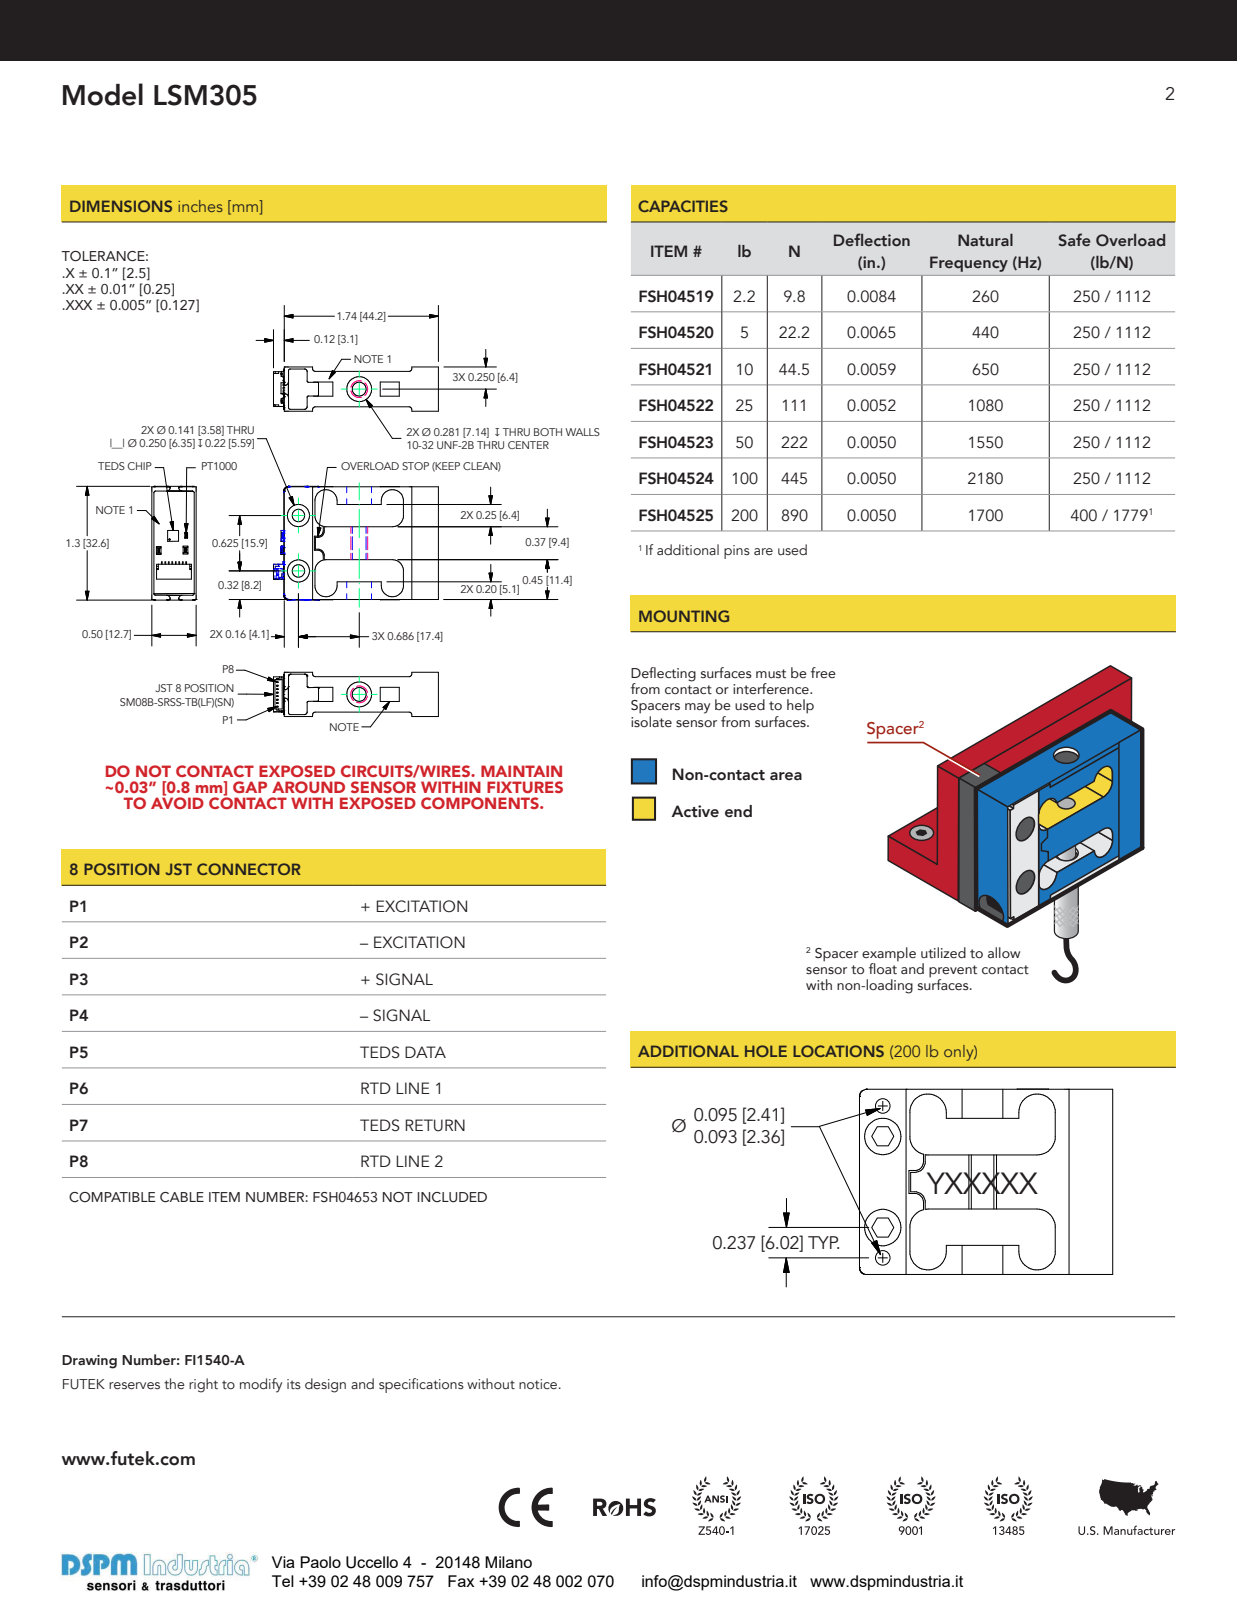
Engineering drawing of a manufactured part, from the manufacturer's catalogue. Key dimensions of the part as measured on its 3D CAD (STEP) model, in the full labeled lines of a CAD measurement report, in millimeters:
Part name (STEP PRODUCT): LSM305
STEP written by: Autodesk Inventor 2020 (AUTOMOTIVE_DESIGN)
Units: millimetres
Bodies: 2 solids, 1542 faces (1180 planar, 47 cylindrical, 315 other)
Overall size (bounding box): 47.3 × 33.3 × 12.7
Volume: 10 900 mm³ · Surface area: 6 613 mm²
Round holes (diameter × count): ⌀3.6 ×2, ⌀6.4 ×2, ⌀0.4 ×1, ⌀4 ×1, ⌀7.1 ×1
Partial cylindrical surfaces — rounded edges, fillets, slot ends (radius × count): R3.2 ×8, R0.1 ×4, R0.8 ×4, R0.5 ×2, R1.2 ×2, R1.3 ×2, R1.3 ×2, R1.5 ×2
Main face-to-face distances: 11.4, 1.3, 10.2, 12.7, 20.9, 44.3, 32.3, 6.4, 9.4, 5.1
Hole centre spacings: 15.9
